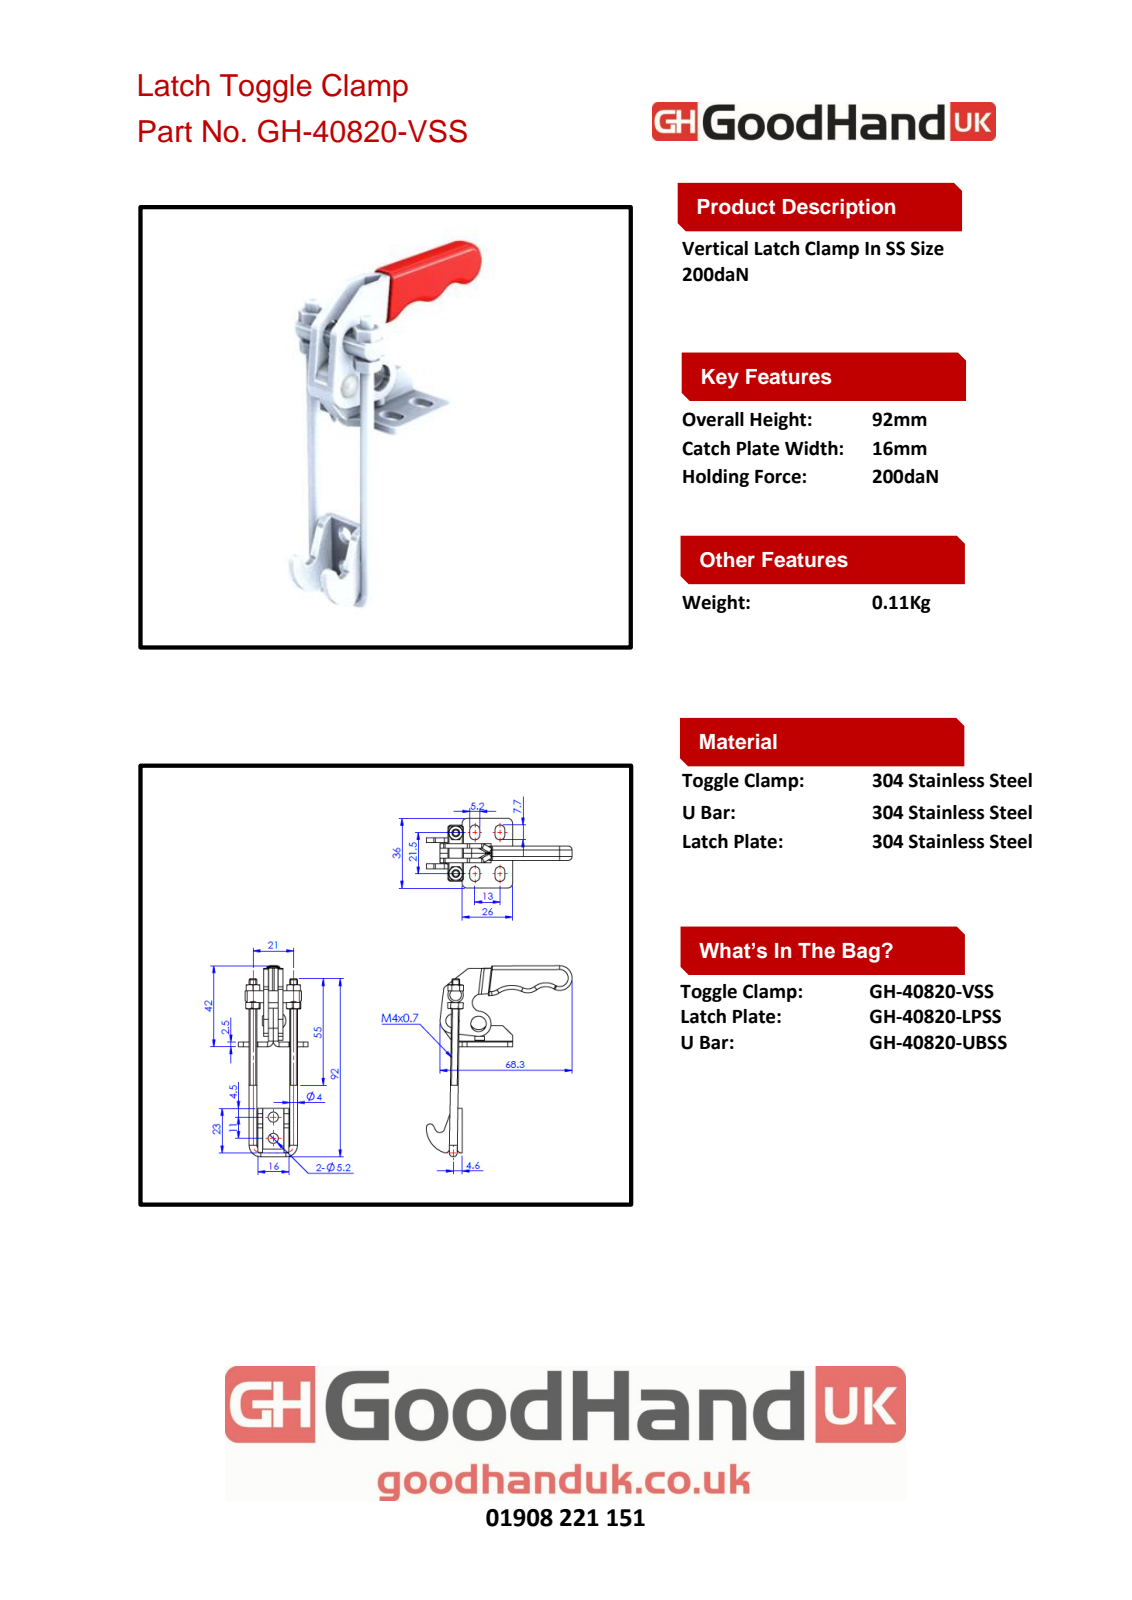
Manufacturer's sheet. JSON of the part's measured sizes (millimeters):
{"part_name": "Group2^GH-40820-V(簡化); Group1^GH-40820(簡化); GH-40820-SSV(簡化); Group1^GH-40820-V(簡化) (+2 more)", "step_written_by": "SolidWorks 2016 (AUTOMOTIVE_DESIGN)", "units": "millimeters", "bodies": {"solids": 7, "faces": 429, "planar": 115, "cylindrical": 152, "other": 162}, "overall_size": [99.35, 75.37, 36], "volume_mm3": 16318, "surface_area_mm2": 13950, "round_holes": [[4, 4], [3.3, 2], [5.2, 2], [8, 2], [3, 1]], "round_bosses_or_shafts": [[4, 3]], "partial_cylinders_radius": [[2, 9], [2.5, 9], [0.5, 8], [2.6, 8], [3, 6], [4.5, 4], [0.1, 2], [6.5, 2]], "face_to_face_distances": [2.5, 7.5, 10.5, 5, 3, 10, 13, 0.5, 5.5, 13.5], "hole_center_spacings": [21, 11, 13.5, 13.51, 19.09]}
